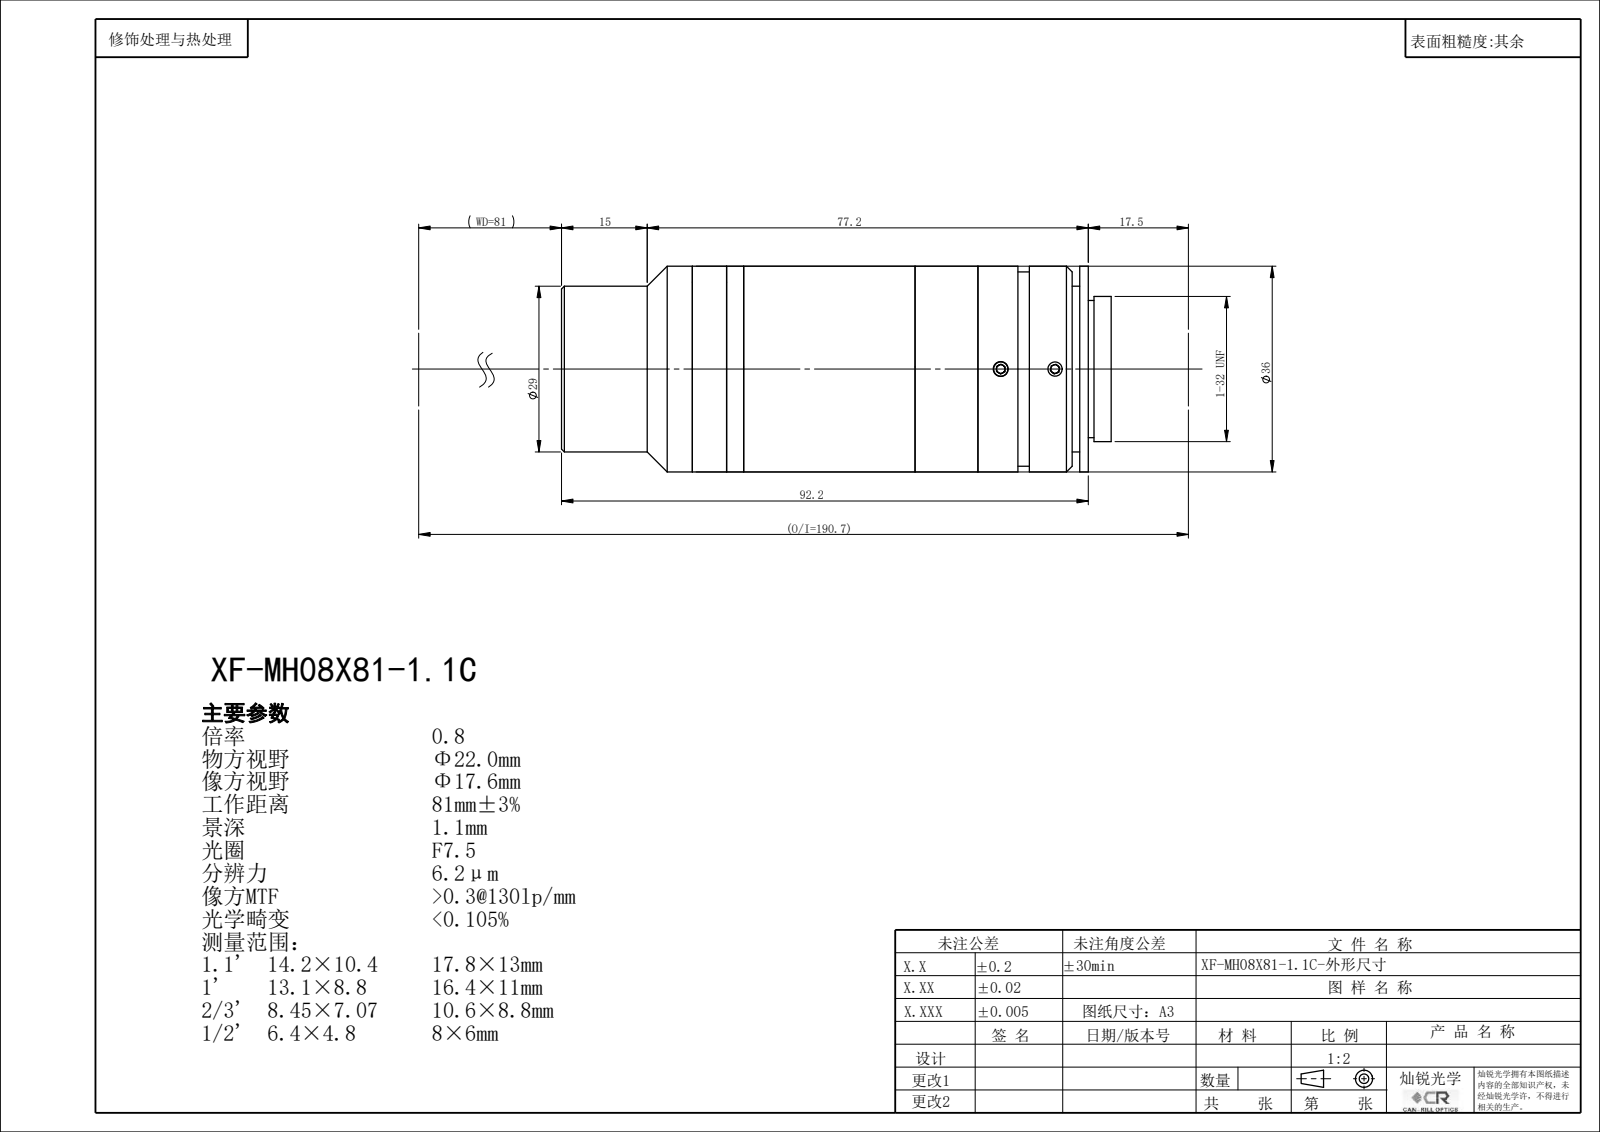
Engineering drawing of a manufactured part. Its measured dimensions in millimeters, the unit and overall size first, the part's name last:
Units: millimetres
Overall size (bounding box): 96.22 × 36 × 36
Round holes (diameter × count): ⌀2.5 ×3, ⌀20 ×1, ⌀22.4 ×1, ⌀24 ×1, ⌀24.9 ×1, ⌀26 ×1, ⌀26.4 ×1
Round bosses / shafts (diameter × count): ⌀36 ×1, ⌀34 ×1, ⌀29 ×1, ⌀25.4 ×1
Main face-to-face distances: 19.32, 1.5, 17.82, 11, 28.82, 30.32, 30, 41, 58.82, 60.32
Bodies: 0 solids, 143 faces (70 planar, 44 cylindrical, 29 other)
Part name (STEP PRODUCT): XF-MH08X81-1.1C
STEP written by: SolidWorks 2022 (CONFIG_CONTROL_DESIGN)
